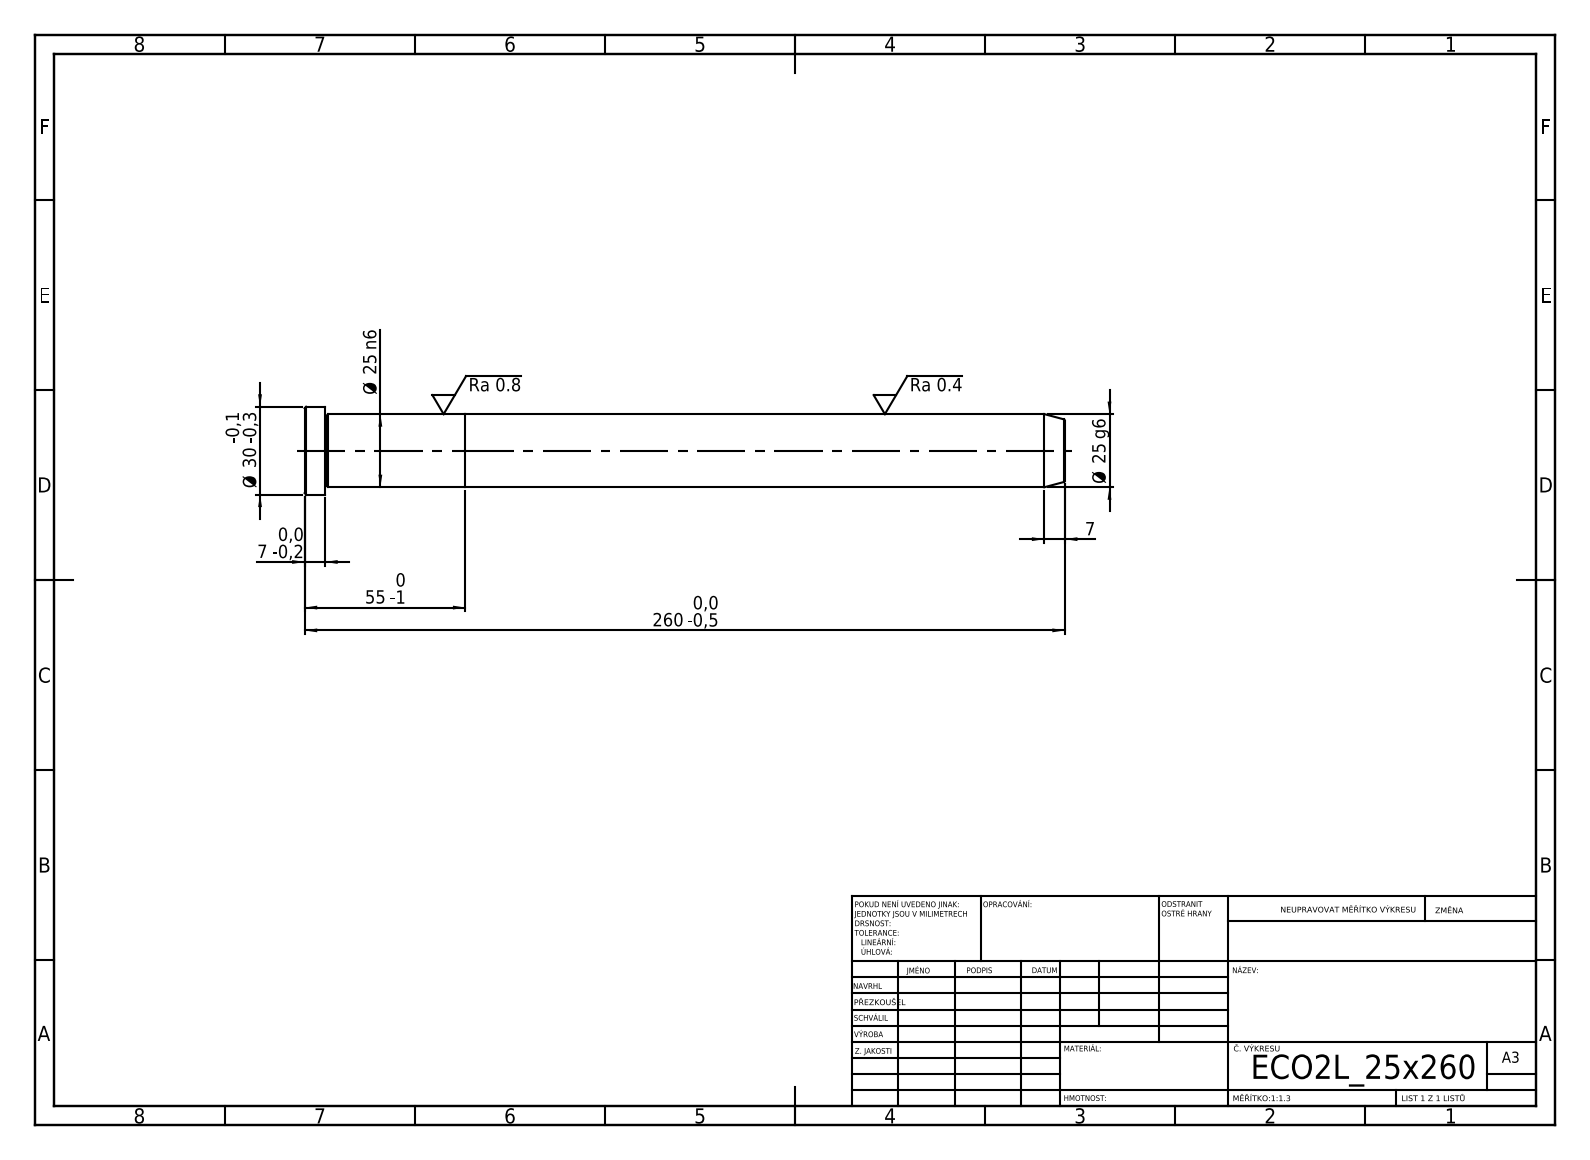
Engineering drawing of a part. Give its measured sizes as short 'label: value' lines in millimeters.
written by: SolidWorks 2019 (CONFIG_CONTROL_DESIGN)
unit: mm
bodies: 2 solids, 21 faces (5 planar, 6 cylindrical, 10 other)
size: 260 × 30 × 30
volume: 128 605 mm³; area: 22 772 mm²
bosses: 1× ⌀30, 1× ⌀25
face distances: 55, 205, 260, 253, 48, 7
